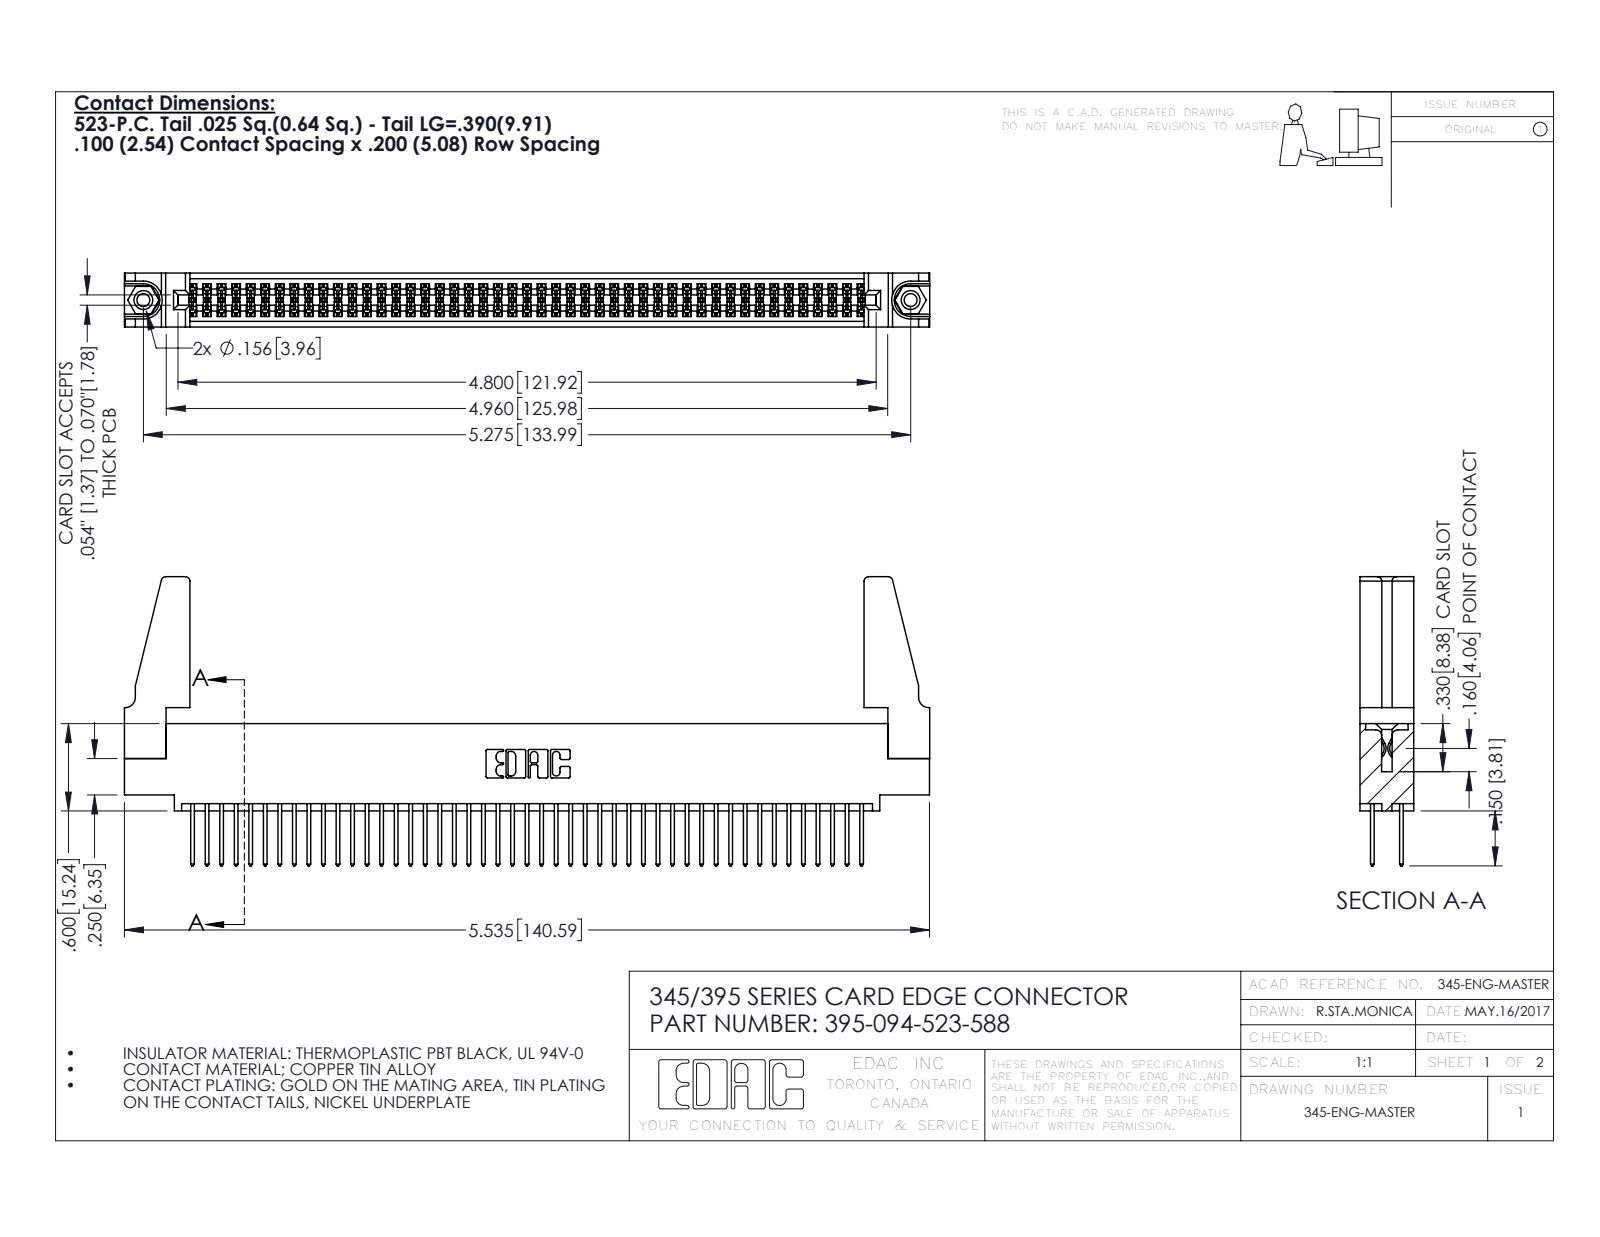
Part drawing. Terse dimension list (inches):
name: 345 Part_0.110 Offset - 0.156 Dia-TH; 395-094-523-588; 345-292-001_345-293-123; 345-220-078_345-220-088 (+1 more)
written by: SolidWorks 2016 (CONFIG_CONTROL_DESIGN)
unit: in
bodies: 99 solids, 4954 faces (3258 planar, 1680 cylindrical, 16 other)
size: 5.536 × 1.987 × 0.37
volume: 1.042 in³; area: 38.15 in²
holes: 2× ⌀0.089, 2× ⌀0.125, 2× ⌀0.156, 1× ⌀0.064
bosses: 2× ⌀0.155
rounds: 141× R0.006, 94× R0.01, 22× R0.01, 8× R0.03, 6× R0.007, 6× R0.031, 3× R0.026, 2× R0.014
face distances: 0.072, 0.298, 0.37, 0.2, 0.098, 0.272, 0.025, 0.225, 0.175, 0.149
hole spacings: 0.27, 5.039, 5.275
